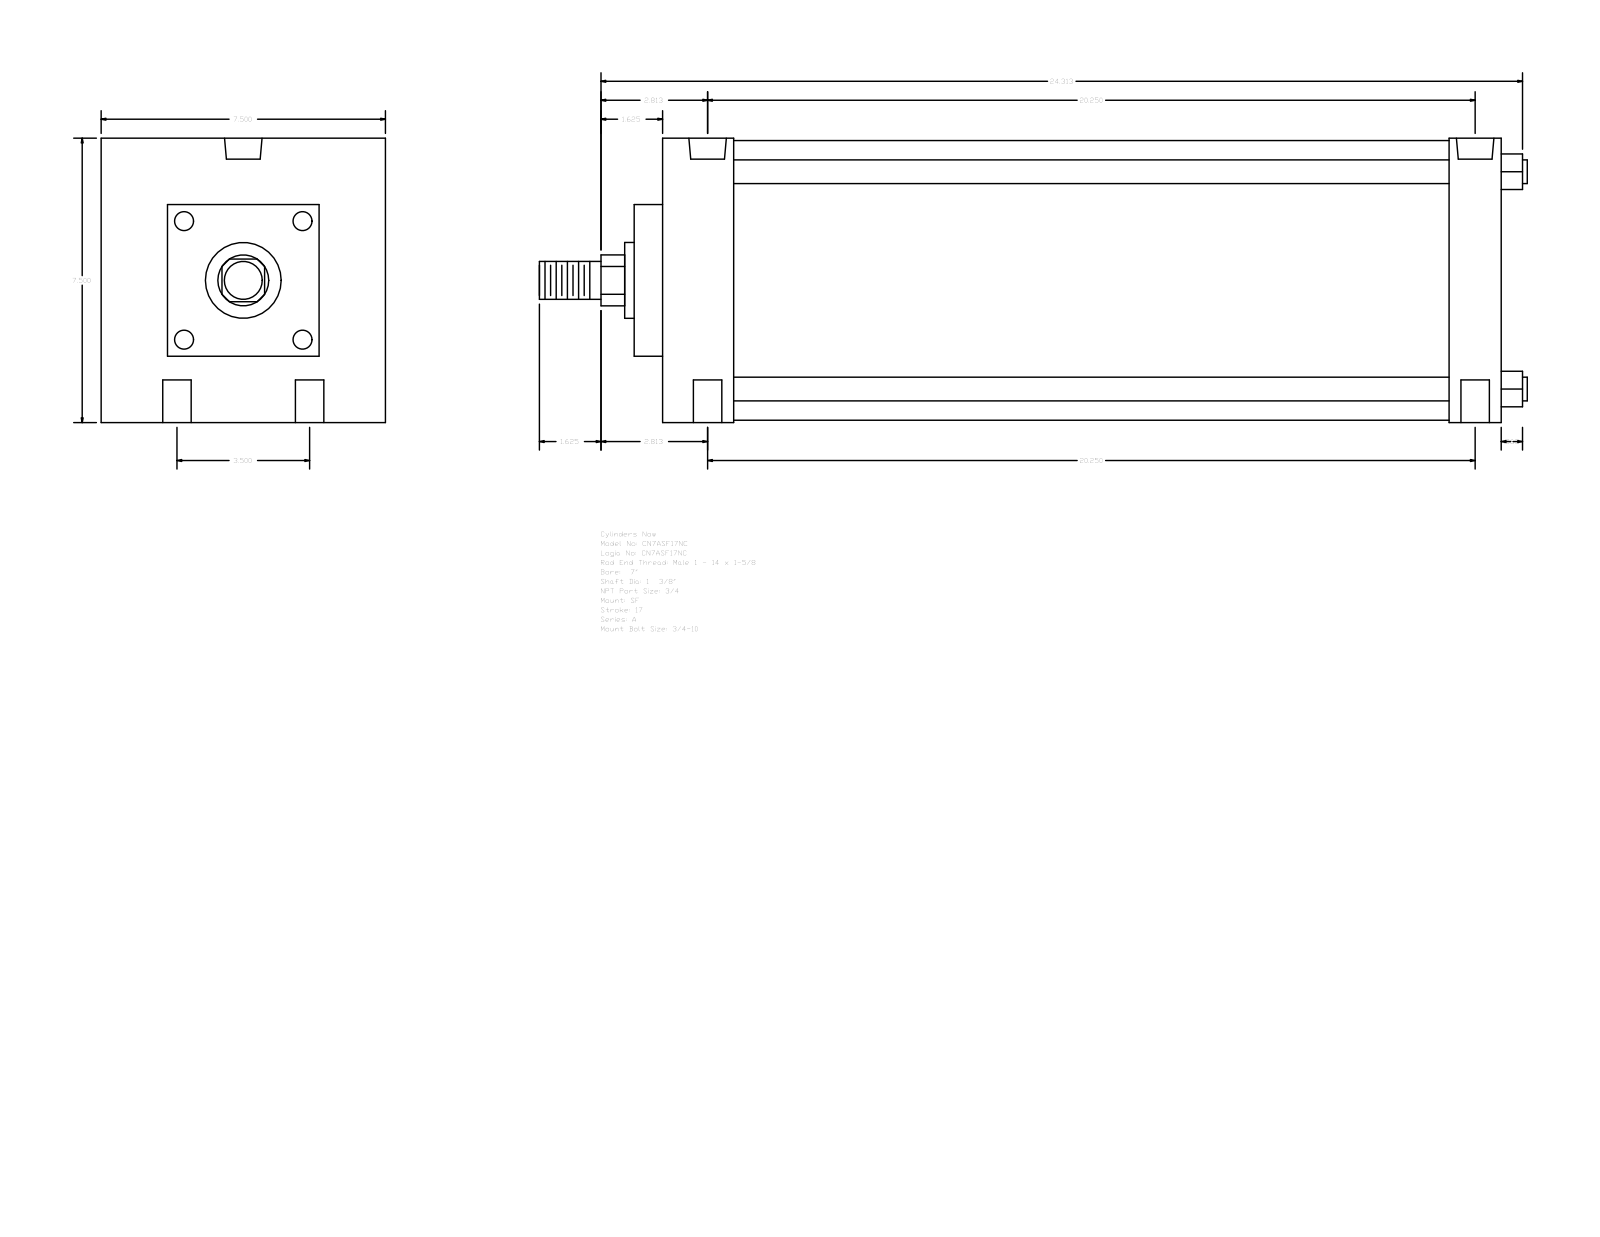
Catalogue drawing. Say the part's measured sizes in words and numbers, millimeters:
The part is named "A_SF__0700_1.375". Its 3-D file was written by "GSSL Pune (CONFIG_CONTROL_DESIGN)". It is 0 solids with 93 faces: 67 planar, 26 cylindrical and 0 other. Overall it measures 661.99 by 190.5 by 190.5 millimeters. Round holes: 4 of diameter 19.05, 2 of diameter 15.08, 2 of diameter 25.12. Round bosses or shafts: 4 of diameter 15.88, 1 of diameter 187.32, 1 of diameter 50.8, 1 of diameter 34.92, 1 of diameter 25.4. Partial cylindrical surfaces (rounded edges, fillets, slot ends): 1 of radius 17.06. The main face-to-face distances are 190.5, 561.98, 19.04, 581.02, 66.67, 546.1, 47.63, 527.06, 479.43, 514.35. The hole center spacings are 44.45, 516.27, 514.35, 88.9, 521.98, 503.23.
